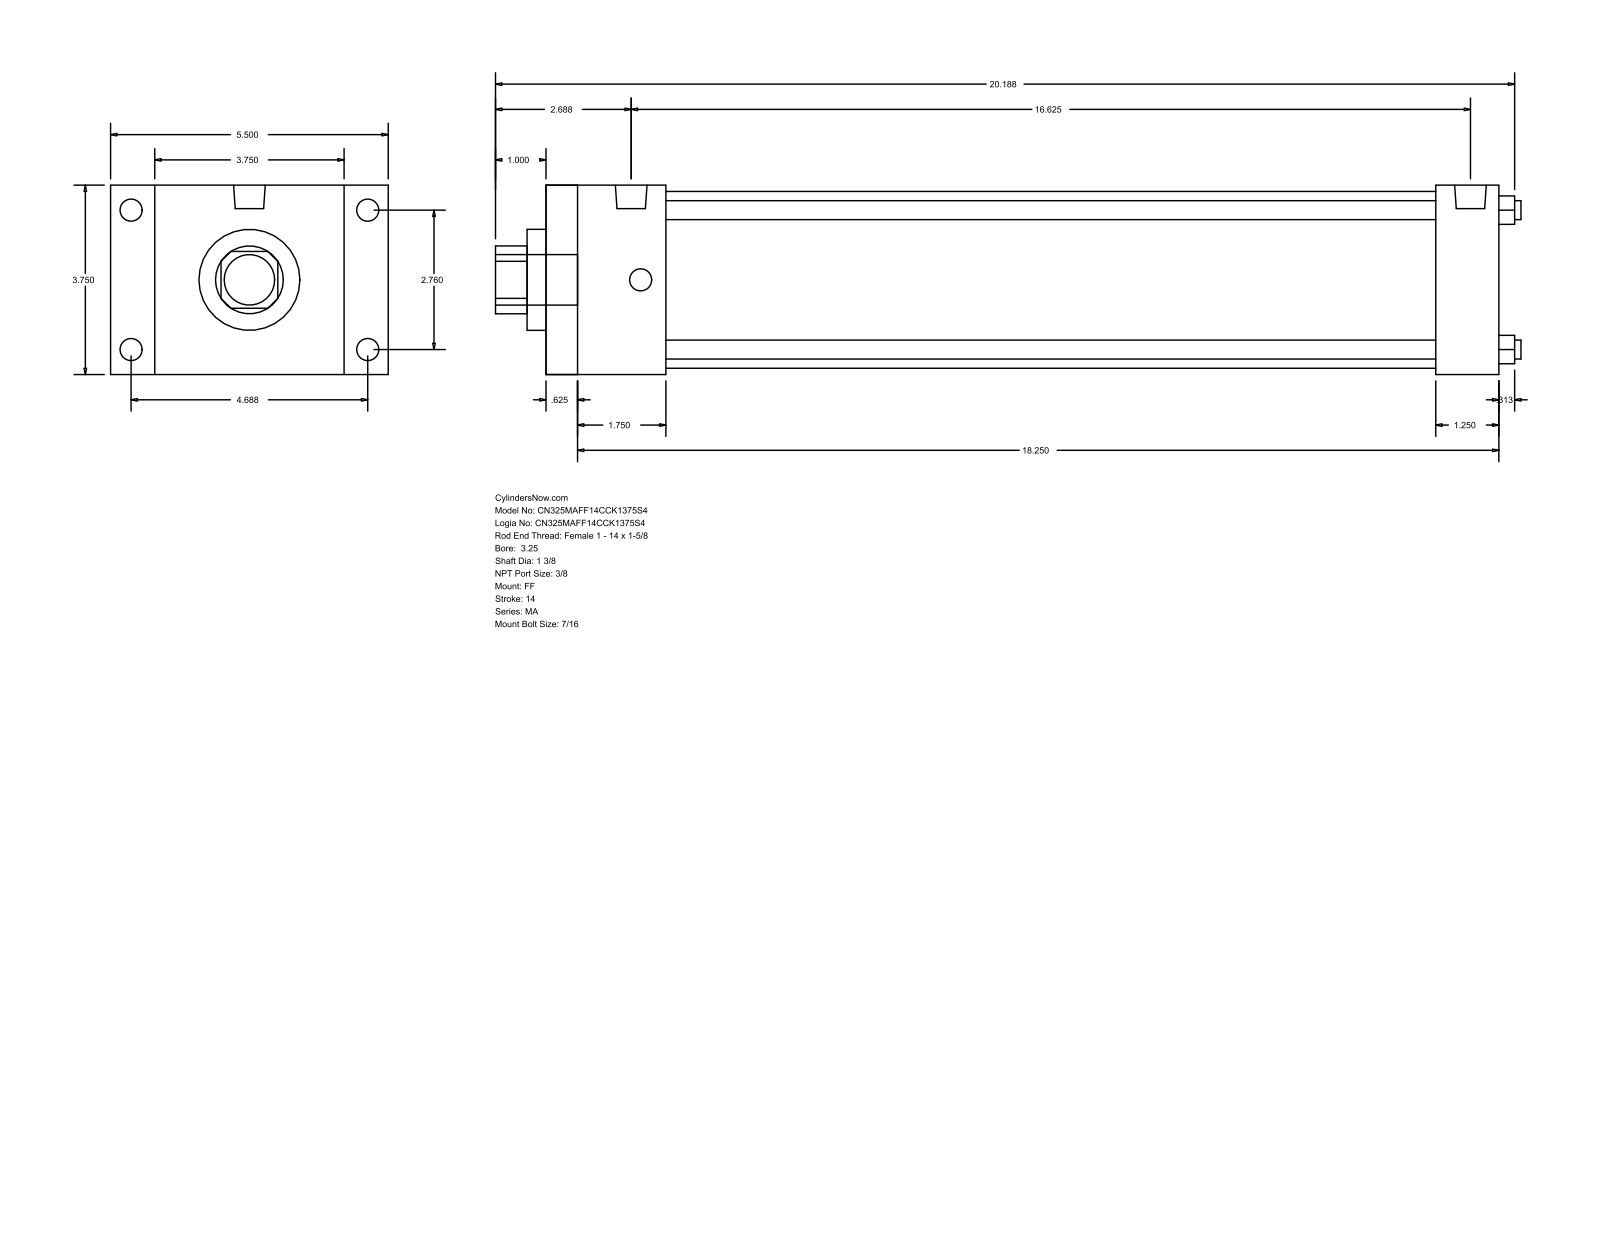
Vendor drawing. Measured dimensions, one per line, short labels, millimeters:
name: MA_FF__0325_1.375
written by: GSSL Pune (CONFIG_CONTROL_DESIGN)
unit: mm
bodies: 0 solids, 92 faces (64 planar, 28 cylindrical, 0 other)
size: 515.94 × 139.7 × 95.25
holes: 4× ⌀9.53, 1× ⌀34.92, 1× ⌀50.8, 1× ⌀88.9
bosses: 8× ⌀11.11, 2× ⌀15.93, 1× ⌀25.4
rounds: 1× R17.06
face distances: 95.24, 479.42, 15.87, 463.55, 22.23, 117.47, 60.32, 447.67, 44.45, 431.8
hole spacings: 49.57, 70.1, 99.14
